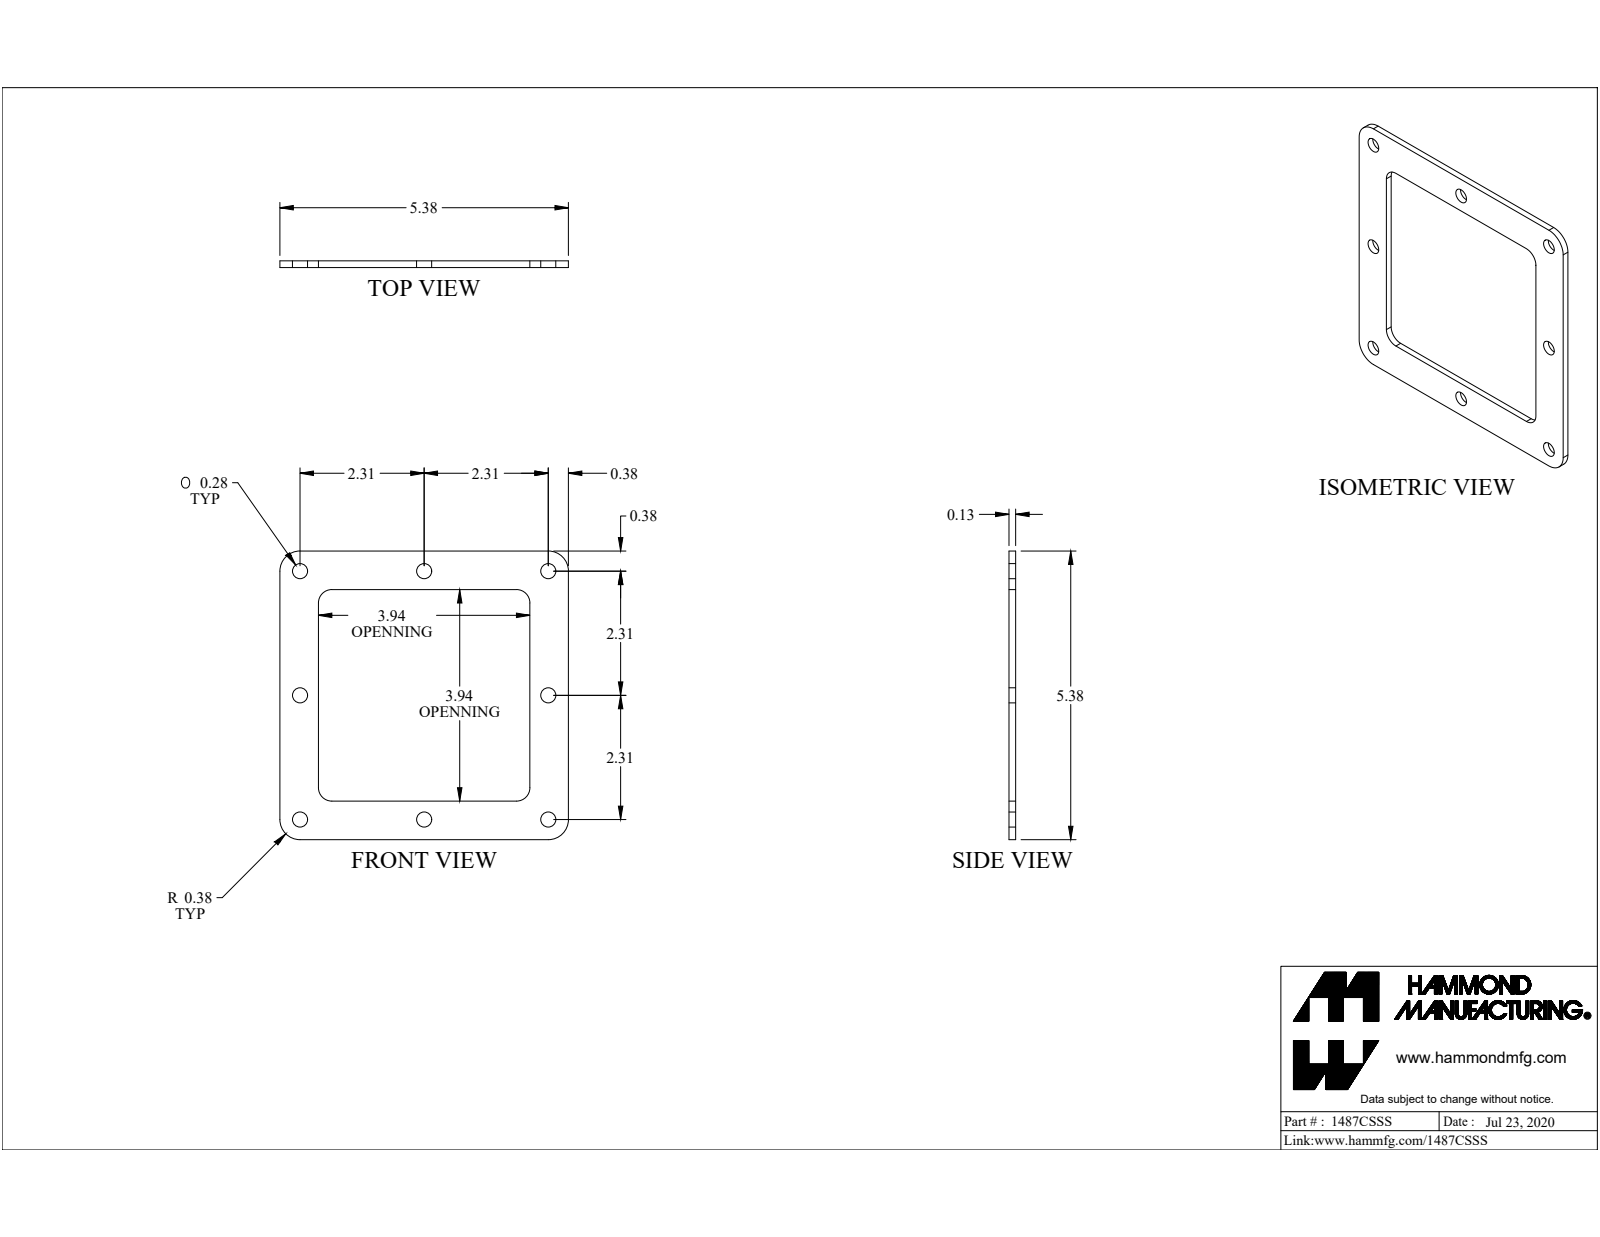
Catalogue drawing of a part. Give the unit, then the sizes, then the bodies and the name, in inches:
Units: inches
Overall size (bounding box): 5.375 × 5.375 × 0.125
Round holes (diameter × count): ⌀0.281 ×8
Partial cylindrical surfaces — rounded edges, fillets, slot ends (radius × count): R0.25 ×4, R0.375 ×4
Main face-to-face distances: 0.125, 0.718, 4.657, 5.375, 3.939
Hole centre spacings: 2.313, 5.171, 4.625, 3.27, 6.541
Volume: 1.601 in³ · Surface area: 31.03 in²
Bodies: 1 solid, 26 faces (10 planar, 16 cylindrical, 0 other)
Part name (STEP PRODUCT): 1487CSSS
STEP written by: SolidWorks 2019 (CONFIG_CONTROL_DESIGN)
